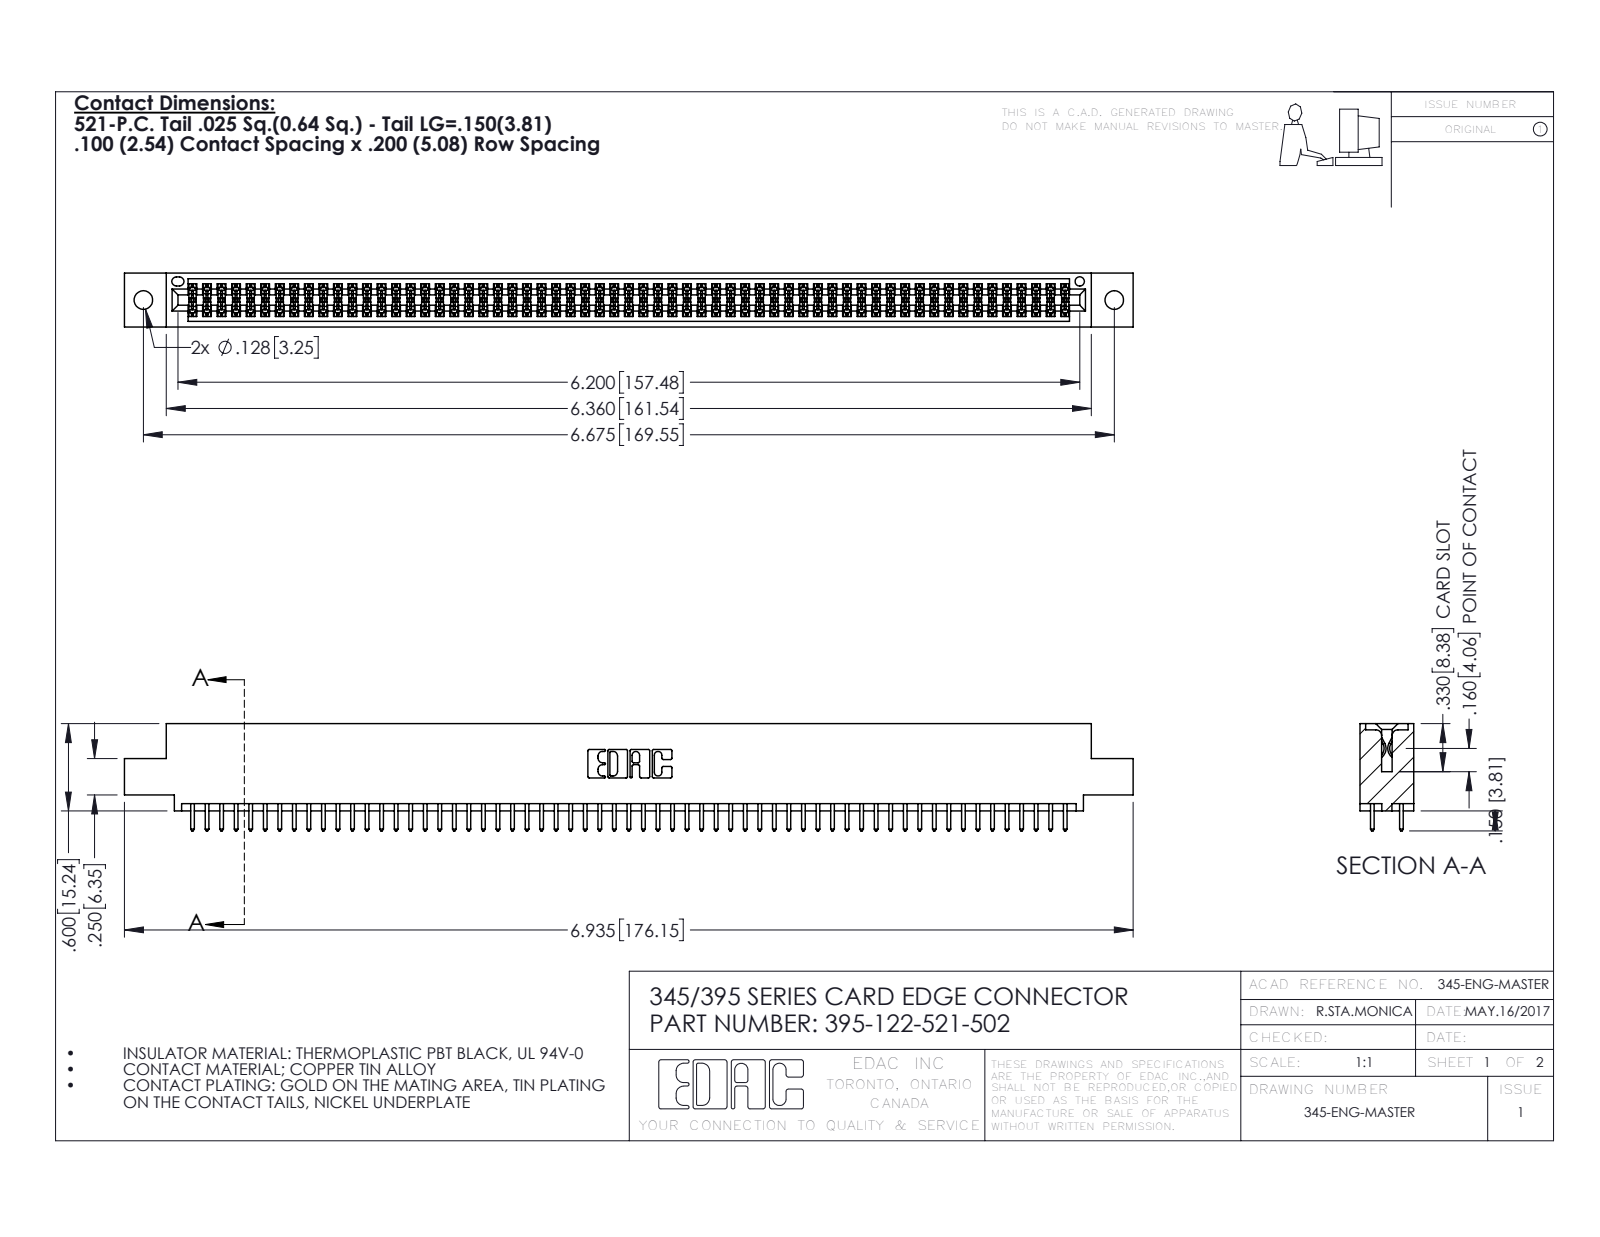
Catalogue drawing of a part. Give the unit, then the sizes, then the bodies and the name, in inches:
Units: inches
Overall size (bounding box): 6.935 × 0.737 × 0.37
Round holes (diameter × count): ⌀0.128 ×2, ⌀0.064 ×1
Partial cylindrical surfaces — rounded edges, fillets, slot ends (radius × count): R0.006 ×183, R0.01 ×122, R0.01 ×22, R0.007 ×6, R0.031 ×6, R0.026 ×3, R0.014 ×2, R0.019 ×2
Main face-to-face distances: 0.298, 0.072, 0.2, 0.098, 0.272, 0.025, 0.37, 0.225, 0.175, 0.149
Hole centre spacings: 0.27, 6.439, 6.675
Volume: 1.045 in³ · Surface area: 39.03 in²
Bodies: 123 solids, 6230 faces (4110 planar, 2120 cylindrical, 0 other)
Part name (STEP PRODUCT): 345-292-001_345-293-121; 395-122-521-502; 345 Part_0.110 Offset - 0.128 Dia
STEP written by: SolidWorks 2016 (CONFIG_CONTROL_DESIGN)
